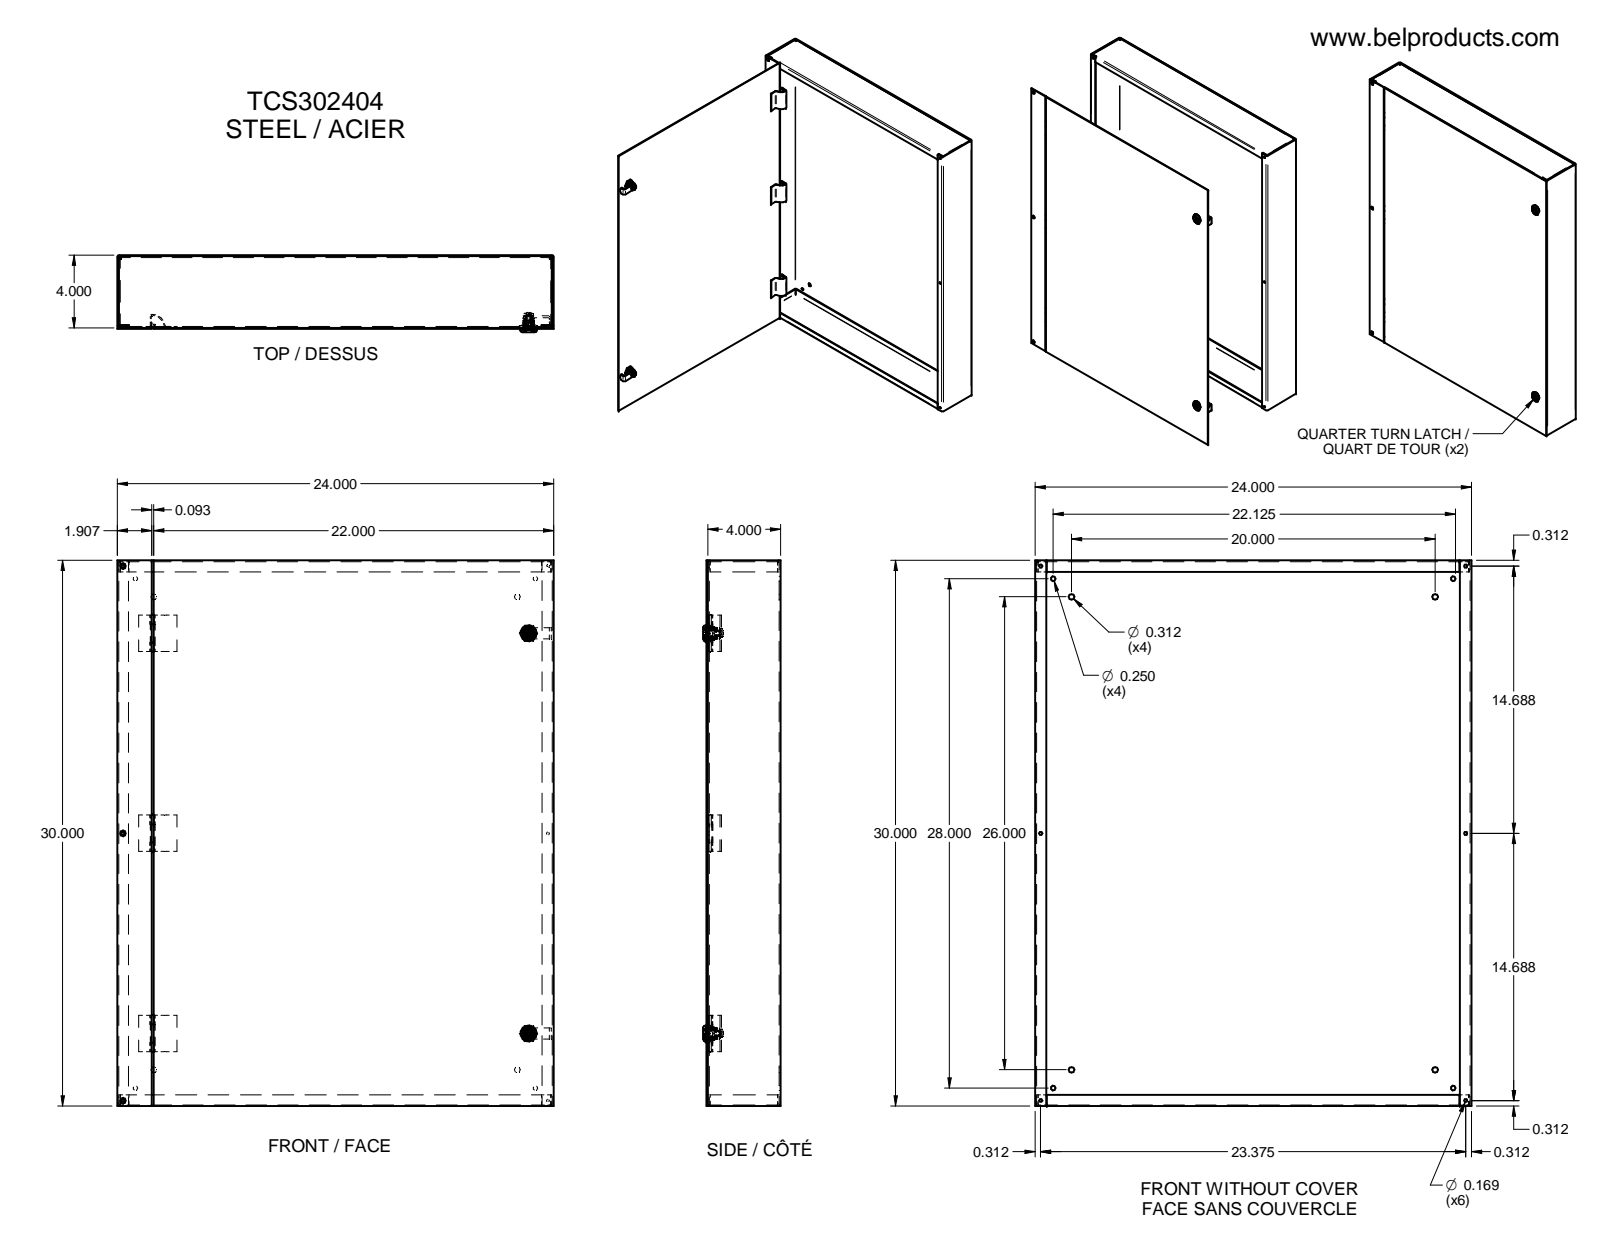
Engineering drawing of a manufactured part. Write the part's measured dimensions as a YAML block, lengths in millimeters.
part_name: "LOCK AVEC TOURNEVIS TYPE 4-12 SANS CAME; HOSING-oa0; INSERT POUR TOURNEVIS-oa1; NOIX DE FIXATION-oa2 (+8 more)"
step_written_by: "Unknown (AUTOMOTIVE_DESIGN)"
units: millimeters
bodies: {solids: 29, faces: 1113, planar: 557, cylindrical: 274, other: 282}
overall_size: [762, 609.6, 107.97]
volume: 2426000
surface_area: 2576000
round_holes:
  - {diameter: 7.92, count: 7}
  - {diameter: 4.29, count: 6}
  - {diameter: 6.35, count: 4}
  - {diameter: 6.99, count: 2}
  - {diameter: 9.1, count: 2}
  - {diameter: 11.18, count: 2}
  - {diameter: 12.83, count: 2}
  - {diameter: 15.8, count: 2}
  - {diameter: 17.46, count: 2}
  - {diameter: 3.81, count: 1}
round_bosses_or_shafts:
  - {diameter: 22.86, count: 2}
  - {diameter: 22.61, count: 2}
  - {diameter: 15.75, count: 2}
  - {diameter: 12.95, count: 2}
  - {diameter: 12.62, count: 2}
  - {diameter: 12.19, count: 2}
  - {diameter: 11.86, count: 2}
  - {diameter: 10.08, count: 2}
partial_cylinders:
  - {radius: 9.53, count: 22}
  - {radius: 0.25, count: 16}
  - {radius: 0.81, count: 13}
  - {radius: 2.72, count: 12}
  - {radius: 9.42, count: 4}
  - {radius: 1.52, count: 2}
  - {radius: 3.05, count: 2}
  - {radius: 6.22, count: 2}
face_to_face_distances: [1.91, 101.6, 99.69, 103.51, 1.9, 607.69, 760.1, 609.6, 605.78, 762]
hole_center_spacings: [24.69, 35.92, 60.61, 332.97, 356.03, 373.06, 534, 552.52]
